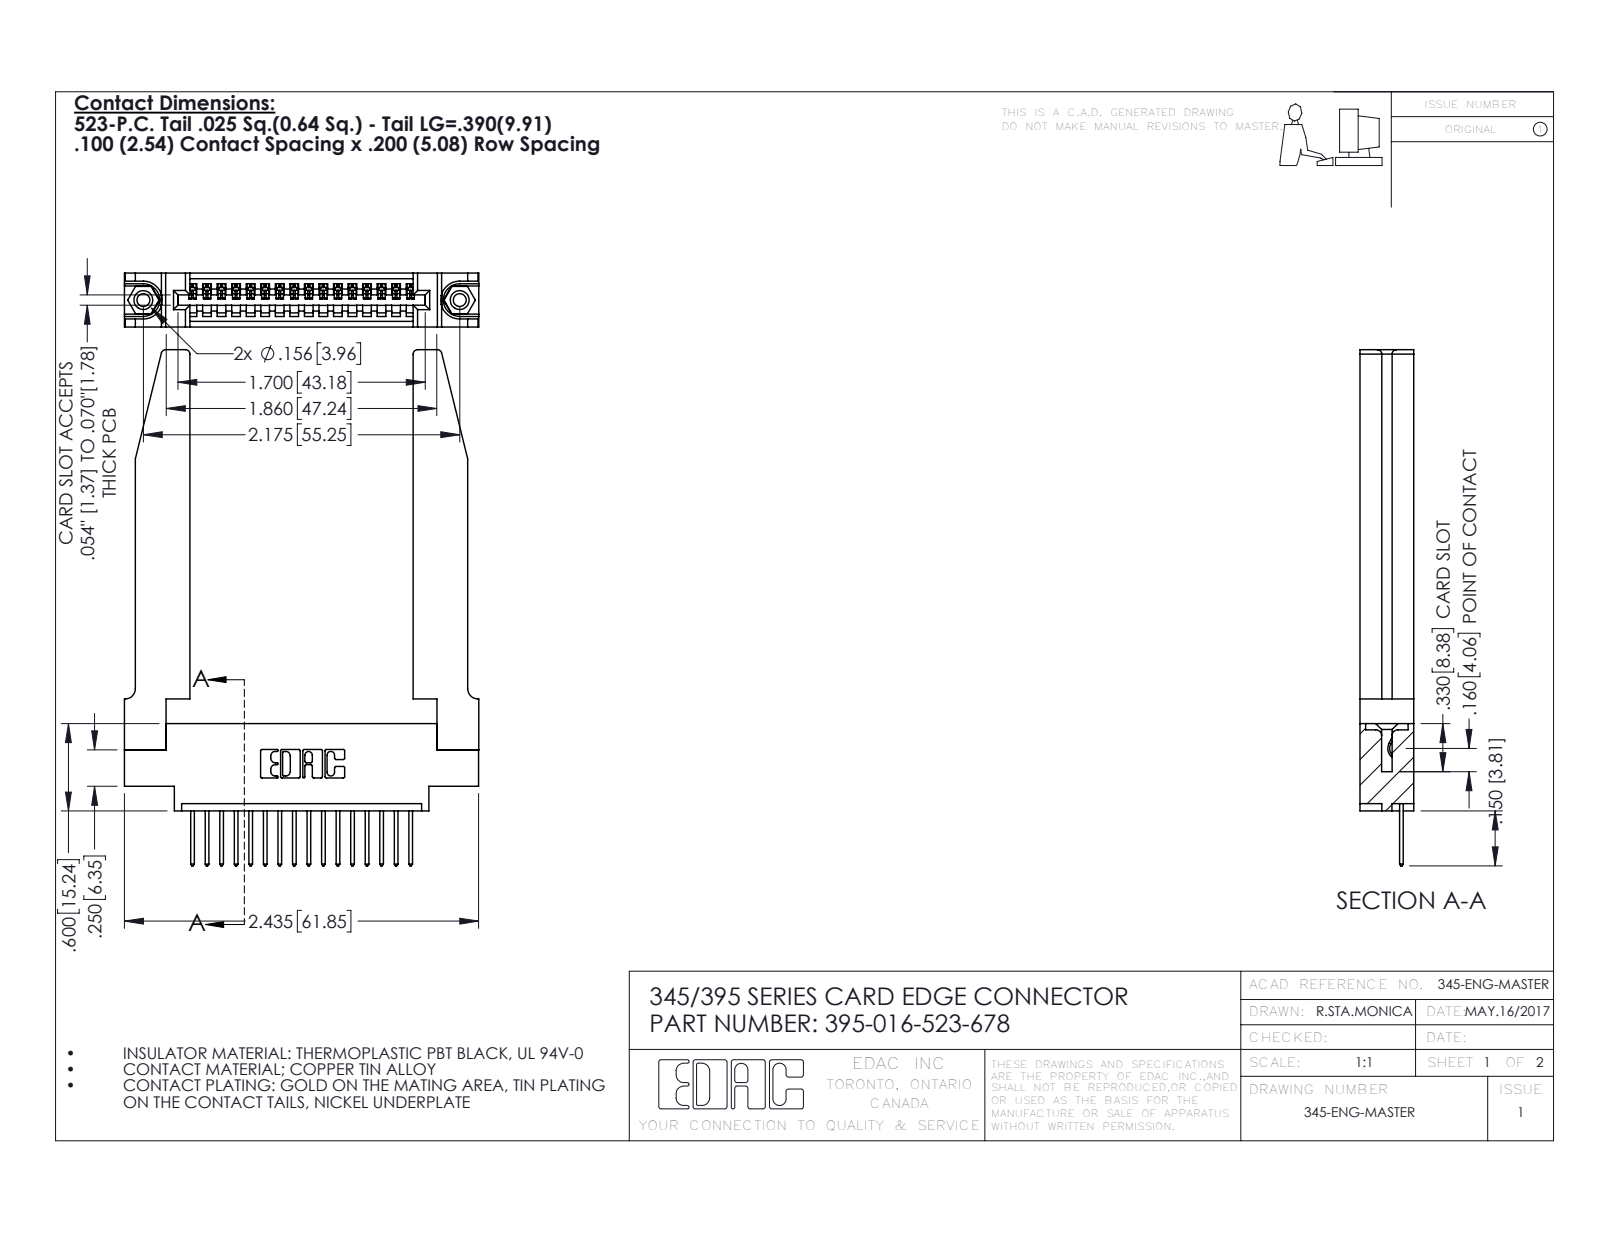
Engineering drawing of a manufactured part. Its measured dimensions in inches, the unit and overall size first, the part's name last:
Units: inches
Overall size (bounding box): 3.547 × 2.436 × 0.37
Round holes (diameter × count): ⌀0.089 ×2, ⌀0.125 ×2, ⌀0.156 ×2, ⌀0.064 ×1
Round bosses / shafts (diameter × count): ⌀0.155 ×2
Partial cylindrical surfaces — rounded edges, fillets, slot ends (radius × count): R0.006 ×32, R0.01 ×32, R0.01 ×22, R0.03 ×8, R0.007 ×6, R0.031 ×6, R0.026 ×3, R0.031 ×2
Main face-to-face distances: 0.37, 0.072, 0.298, 0.148, 0.15, 0.098, 0.272, 0.025, 0.2, 0.22
Hole centre spacings: 0.27, 1.942, 2.175
Volume: 0.813 in³ · Surface area: 21.71 in²
Bodies: 21 solids, 1292 faces (866 planar, 374 cylindrical, 52 other)
Part name (STEP PRODUCT): 395-016-523-678; 345-292-001_345-293-123; 345-250-001_345-250-001-102; 345 Part_0.170 Offset - 0.156 Dia-TH (+1 more)
STEP written by: SolidWorks 2016 (CONFIG_CONTROL_DESIGN)
